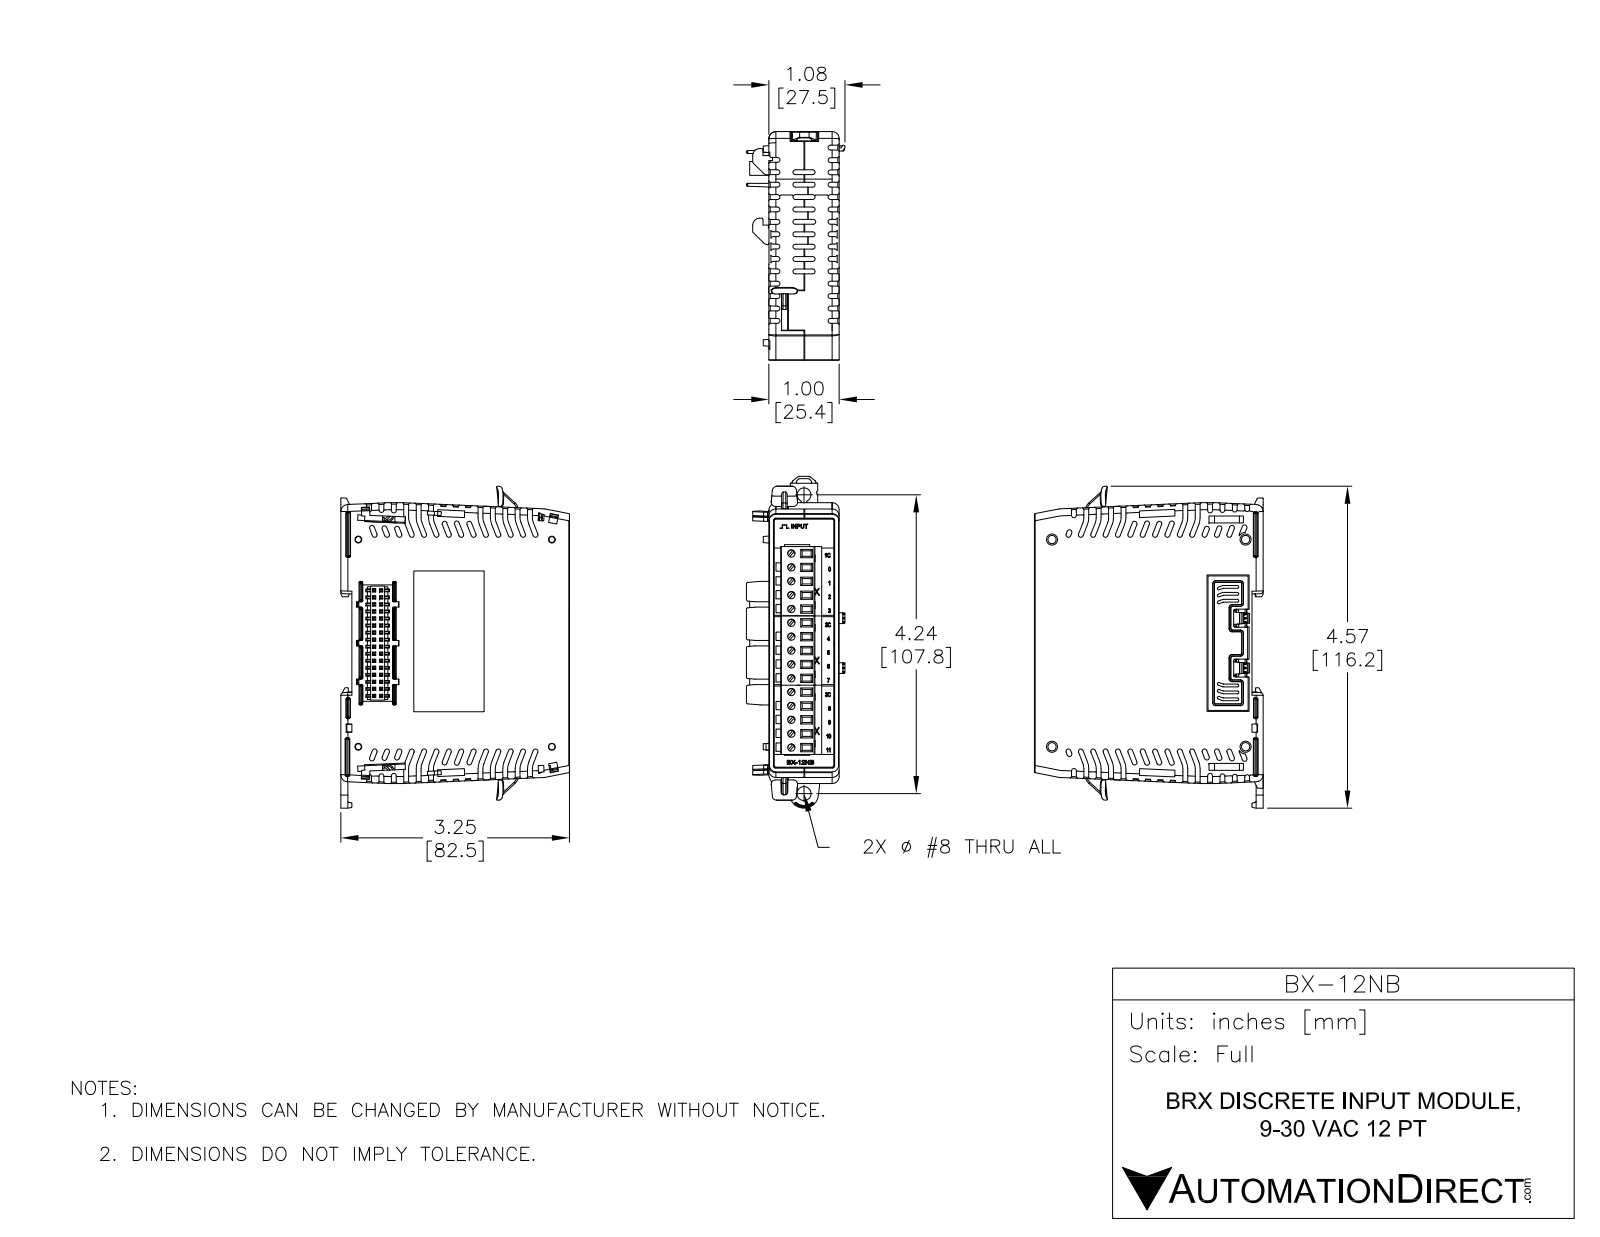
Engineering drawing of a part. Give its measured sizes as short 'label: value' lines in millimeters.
name: BX-12NB
written by: SolidWorks 2017 (AUTOMOTIVE_DESIGN)
unit: mm
bodies: 15 solids, 3751 faces (2657 planar, 573 cylindrical, 521 other)
size: 116.5 × 84.1 × 35.6
volume: 190 100 mm³; area: 46 960 mm²
holes: 2× ⌀1.2, 2× ⌀1.7, 2× ⌀3, 2× ⌀3, 1× ⌀5.1
bosses: 2× ⌀1.6, 2× ⌀1.5
rounds: 102× R0.1, 47× R0.3, 34× R0.5, 24× R0.1, 21× R0.2, 15× R3.1, 14× R3, 13× R1
face distances: 25.4, 81.6, 2.5, 81.8, 12.1, 4, 77.5, 77.8, 20, 16
hole spacings: 2.5, 20.9, 23.3, 33, 53.2, 55.7, 65.7, 66.5
